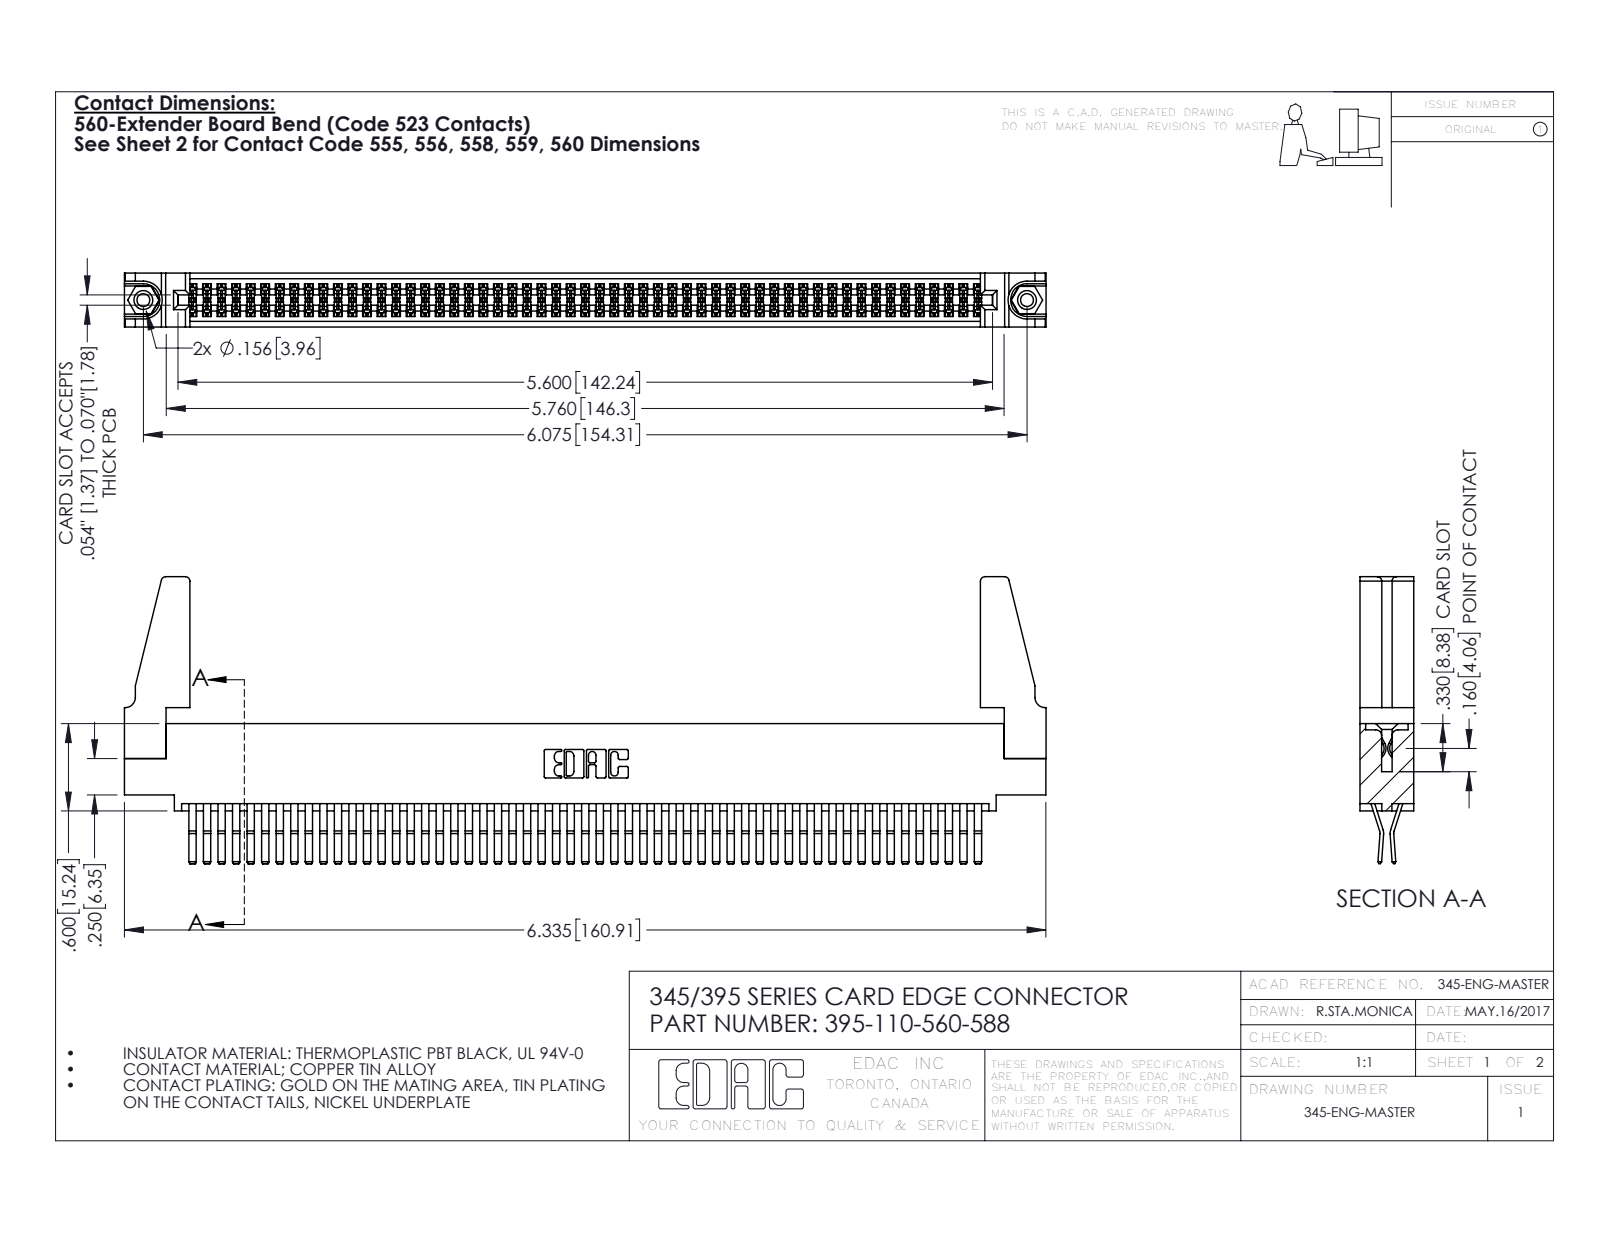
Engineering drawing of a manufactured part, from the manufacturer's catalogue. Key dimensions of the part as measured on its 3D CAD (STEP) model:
Part name (STEP PRODUCT): 345-250-001_345-250-001-102; 345-220-078_345-220-088; 345-292-001_560 Tail; 395-110-560-588 (+1 more)
STEP written by: SolidWorks 2016 (CONFIG_CONTROL_DESIGN)
Units: inches
Bodies: 115 solids, 5974 faces (3786 planar, 2172 cylindrical, 16 other)
Overall size (bounding box): 6.336 × 1.972 × 0.37
Volume: 1.199 in³ · Surface area: 45.83 in²
Round holes (diameter × count): ⌀0.089 ×2, ⌀0.125 ×2, ⌀0.156 ×2, ⌀0.064 ×1
Round bosses / shafts (diameter × count): ⌀0.155 ×2
Partial cylindrical surfaces — rounded edges, fillets, slot ends (radius × count): R0.006 ×165, R0.01 ×22, R0.03 ×8, R0.007 ×6, R0.031 ×6, R0.026 ×3, R0.01 ×2, R0.014 ×2
Main face-to-face distances: 0.072, 0.298, 0.025, 0.37, 0.2, 0.098, 0.272, 0.225, 0.175, 0.149
Hole centre spacings: 0.27, 5.839, 6.075
